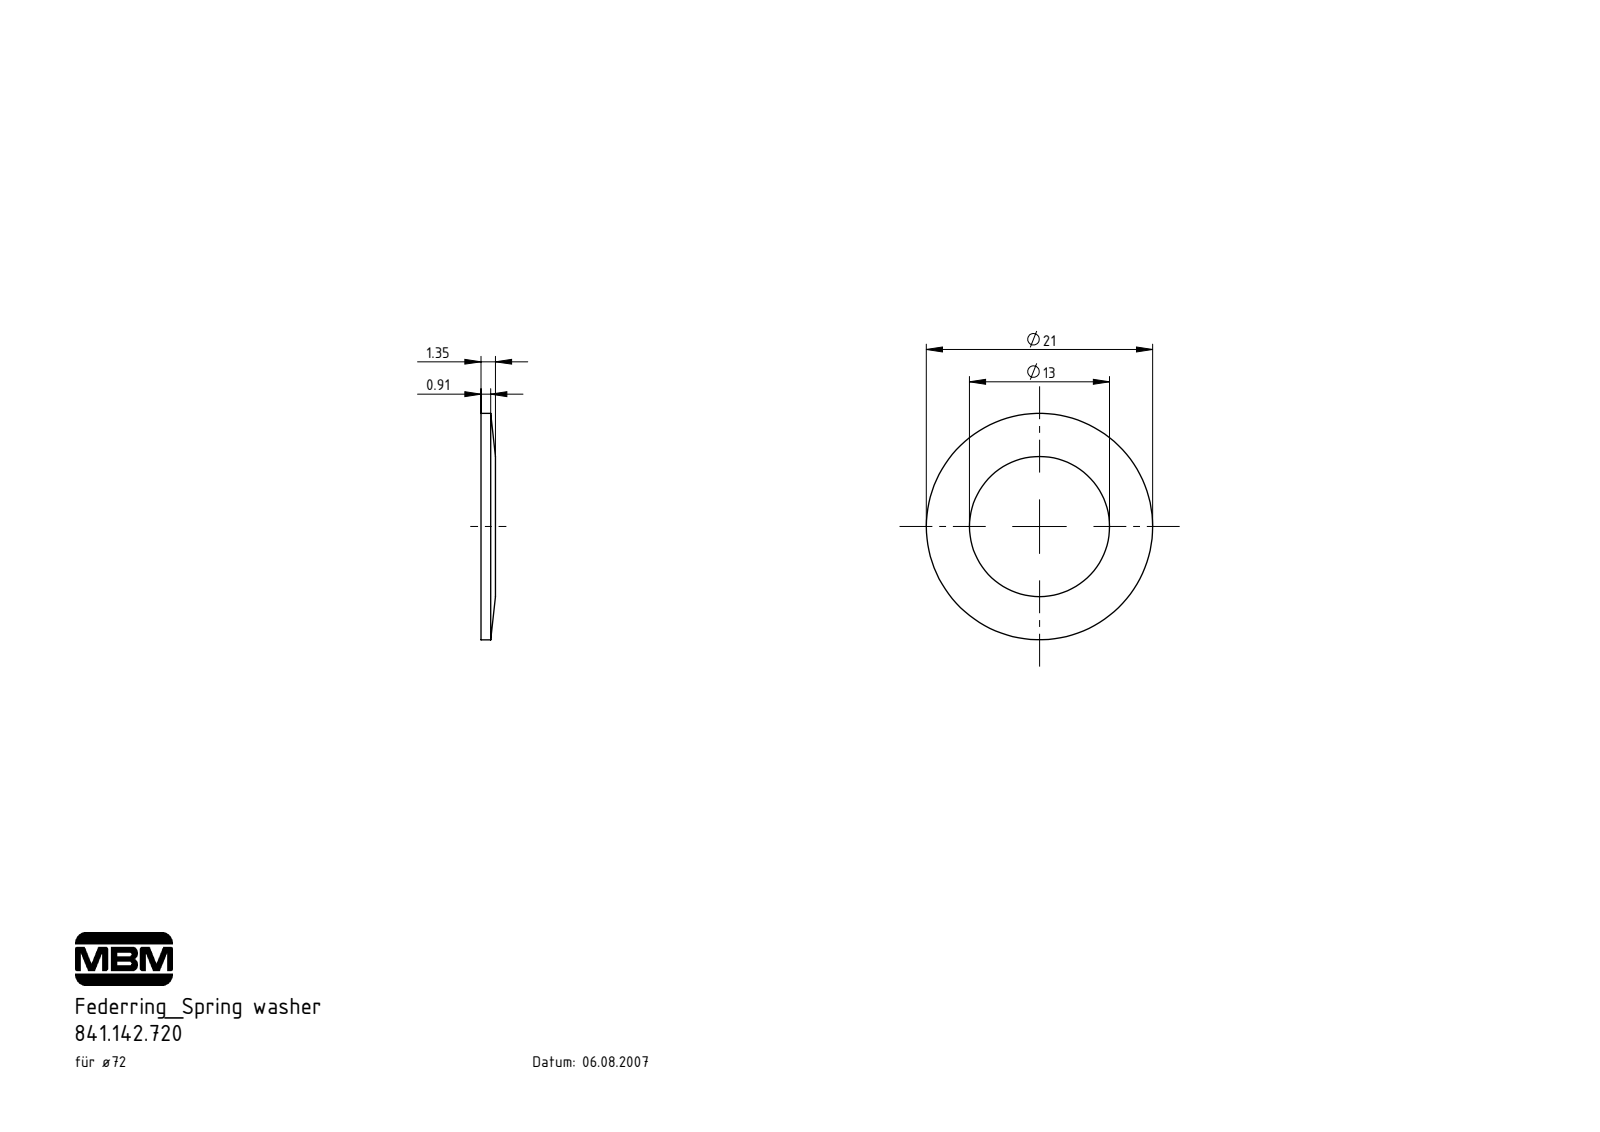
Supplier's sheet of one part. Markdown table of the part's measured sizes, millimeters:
| quantity | value |
| --- | --- |
| part name | 841.142.720 |
| STEP written by | SolidWorks 2022 (AUTOMOTIVE_DESIGN) |
| units | millimeters |
| bodies | 1 solid, 6 faces (2 planar, 4 cylindrical, 0 other) |
| overall size | 21 × 21 × 0.9 |
| volume | 192 mm³ |
| surface area | 523 mm² |
| round holes (diameter × count) | 13 × 1 |
| round bosses / shafts (diameter × count) | 21 × 1 |
| main face-to-face distances | 0.9 |
